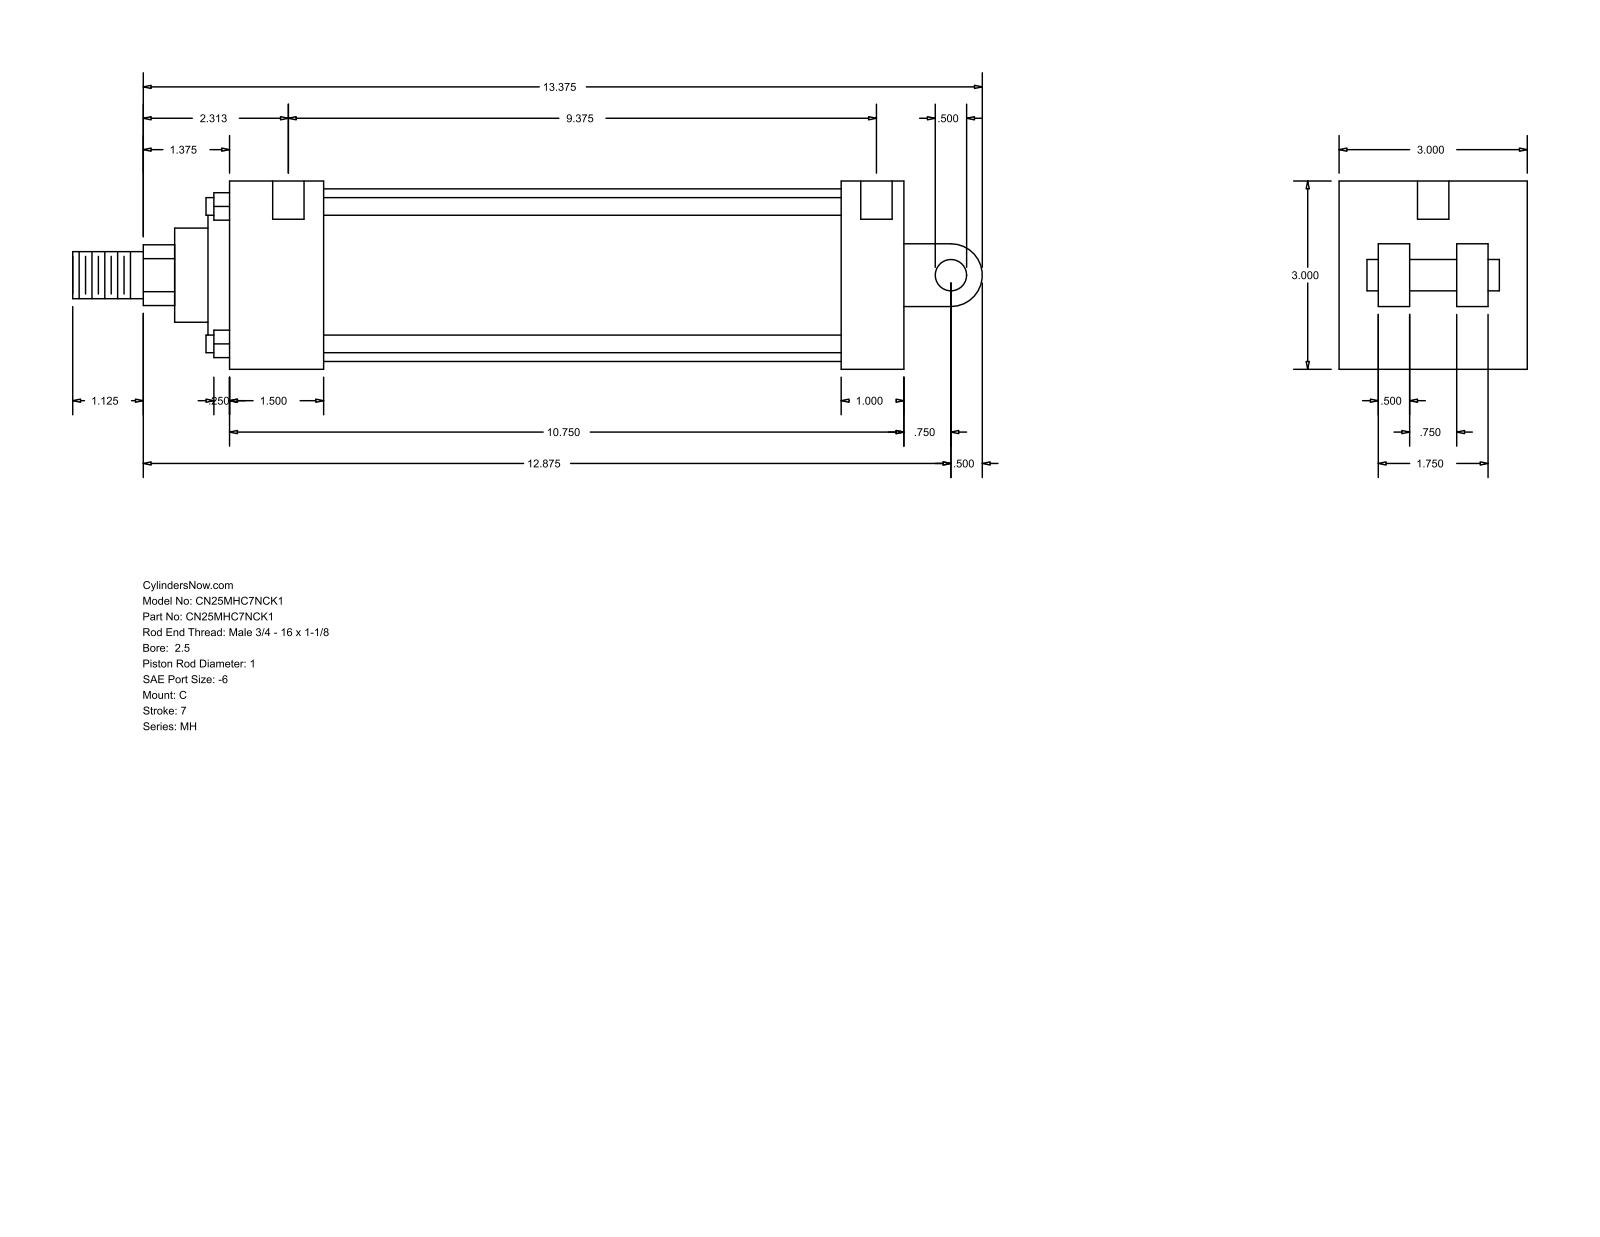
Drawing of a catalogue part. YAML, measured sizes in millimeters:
part_name: "MH_C__0250_1"
step_written_by: "GSSL Pune (CONFIG_CONTROL_DESIGN)"
units: millimeters
bodies: {solids: 0, faces: 101, planar: 71, cylindrical: 30, other: 0}
overall_size: [368.3, 76.2, 76.2]
round_holes:
  - {diameter: 5.56, count: 4}
  - {diameter: 12.7, count: 2}
round_bosses_or_shafts:
  - {diameter: 7.14, count: 4}
  - {diameter: 69.85, count: 1}
  - {diameter: 60.33, count: 1}
  - {diameter: 38.1, count: 1}
  - {diameter: 25.4, count: 1}
  - {diameter: 19.05, count: 1}
  - {diameter: 12.7, count: 1}
partial_cylinders:
  - {radius: 12.29, count: 1}
  - {radius: 12.7, count: 1}
face_to_face_distances: [76.2, 273.06, 60.33, 15.87, 247.65, 25.41, 38.11, 209.54, 234.95, 12.7]
hole_center_spacings: [246.06, 3.18, 4.76, 238.12, 241.3, 242.88]
